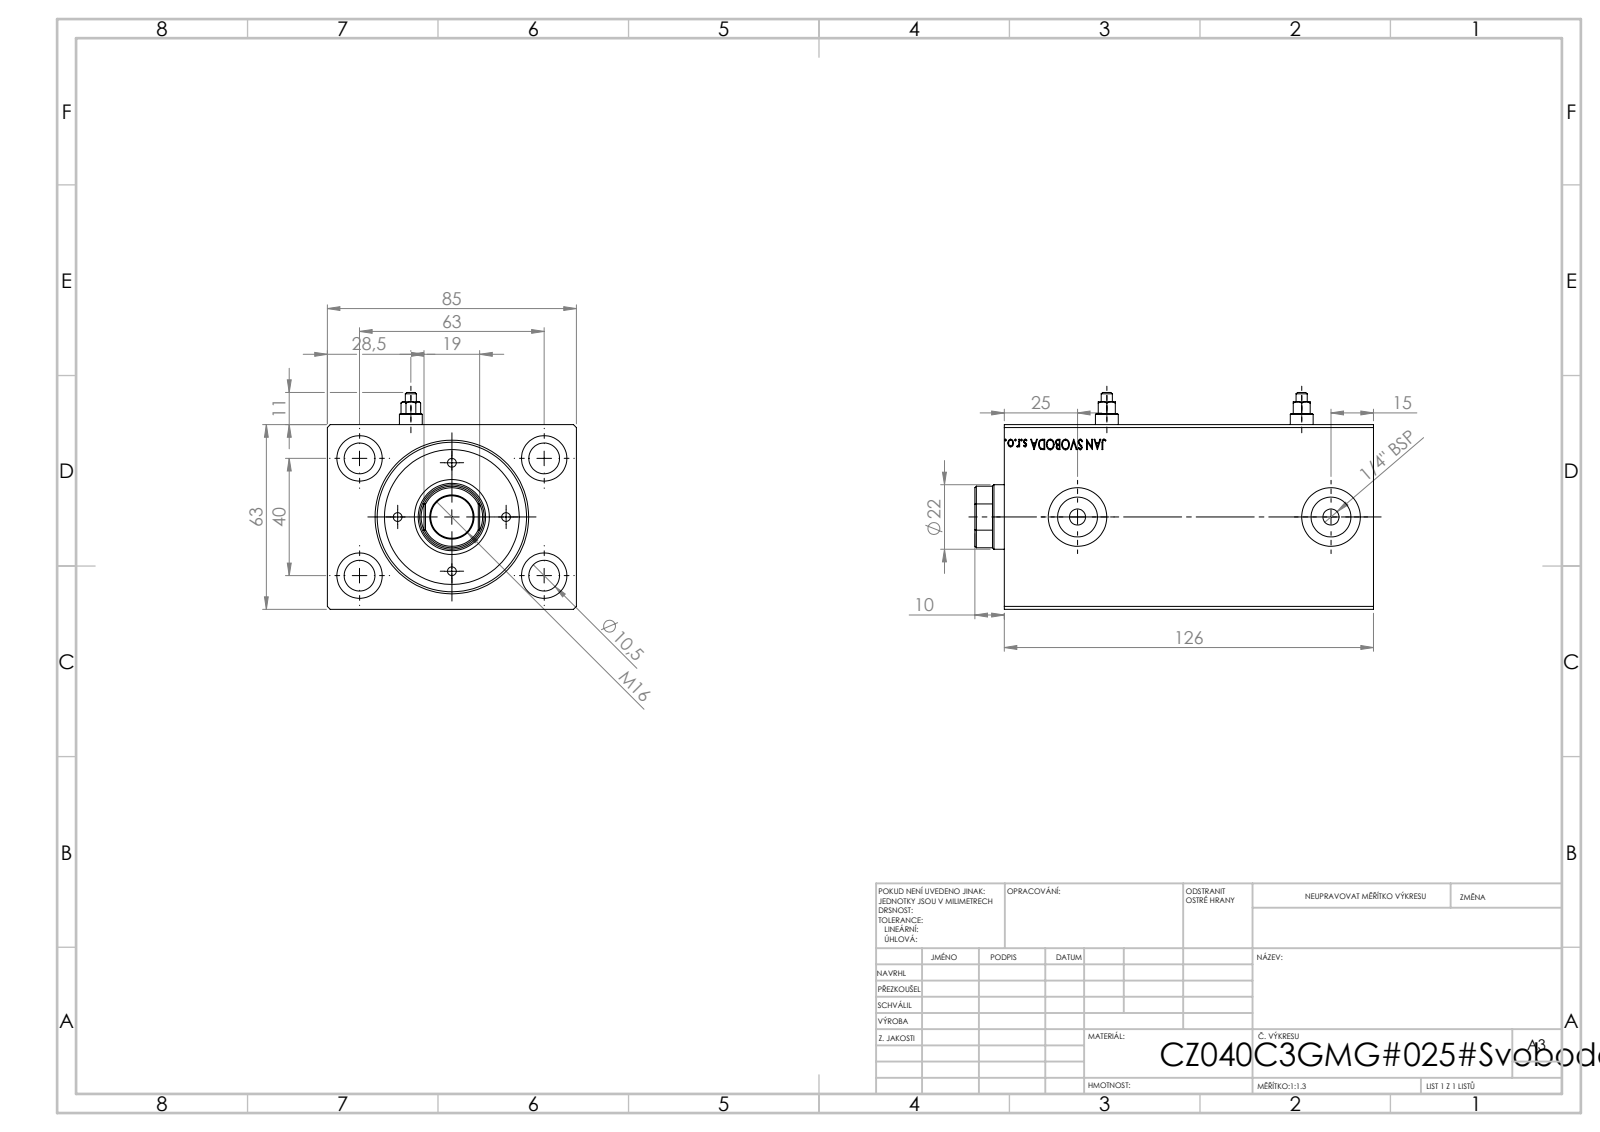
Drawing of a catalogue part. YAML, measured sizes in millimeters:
step_written_by: "SolidWorks 2019 (CONFIG_CONTROL_DESIGN)"
units: millimeters
bodies: {solids: 1, faces: 825, planar: 397, cylindrical: 46, other: 382}
overall_size: [126, 85, 63]
volume: 470828
surface_area: 80761
round_holes:
  - {diameter: 10.5, count: 4}
  - {diameter: 15.5, count: 4}
  - {diameter: 5.5, count: 2}
  - {diameter: 8, count: 2}
  - {diameter: 13.6, count: 2}
  - {diameter: 20, count: 2}
  - {diameter: 36, count: 1}
  - {diameter: 40, count: 1}
  - {diameter: 51, count: 1}
face_to_face_distances: [63, 85, 126, 110.7, 15.3, 125.8, 15.1, 10.33, 115.67, 10]
hole_center_spacings: [37.31, 40, 63, 74.63, 66.5, 86.5]
